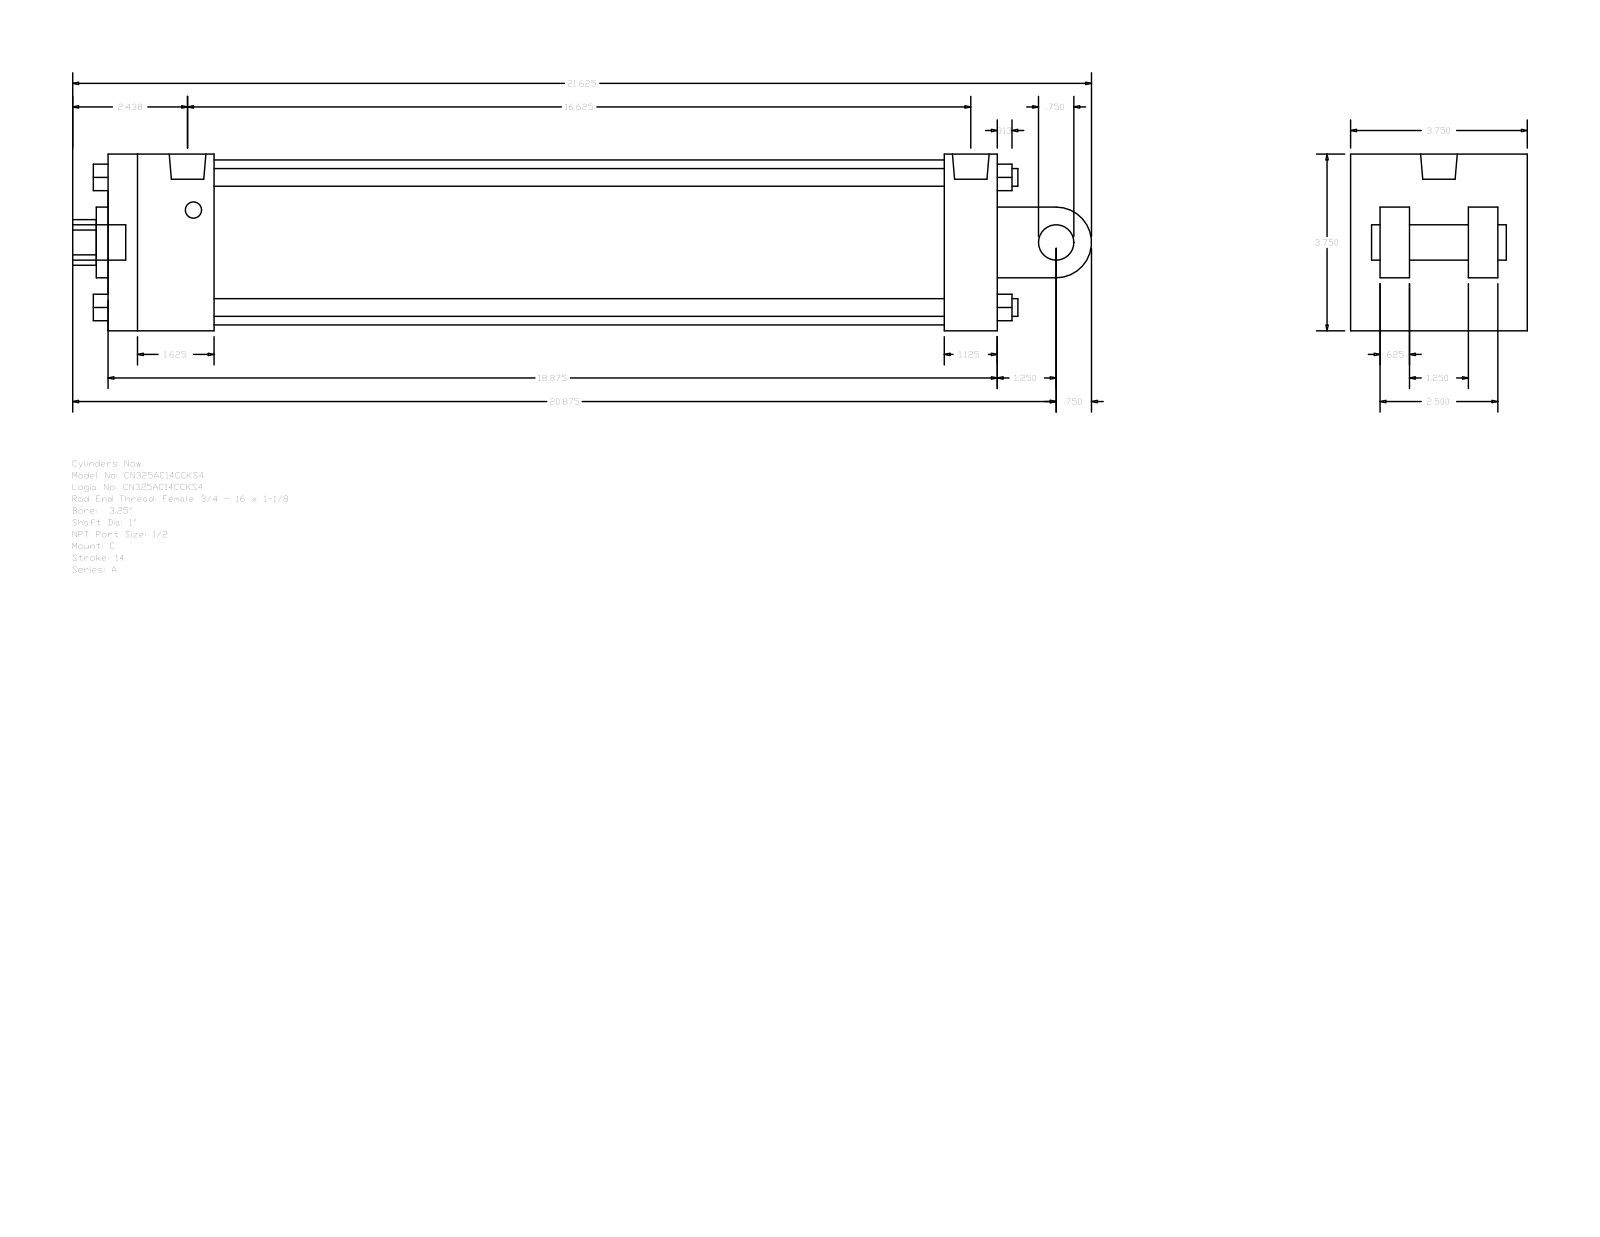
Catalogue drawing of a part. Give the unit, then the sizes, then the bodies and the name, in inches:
Units: inches
Overall size (bounding box): 21.625 × 3.75 × 3.75
Round holes (diameter × count): ⌀0.344 ×2, ⌀0.778 ×1, ⌀1 ×1, ⌀1.5 ×1, ⌀3.5 ×1
Round bosses / shafts (diameter × count): ⌀0.375 ×4, ⌀0.75 ×2, ⌀0.344 ×2, ⌀0.778 ×1
Partial cylindrical surfaces — rounded edges, fillets, slot ends (radius × count): R0.484 ×1, R0.75 ×1
Main face-to-face distances: 3.75, 18.875, 0.625, 2.5, 1.875, 3.125, 1.25, 2.625, 17.75, 1.125
Hole centre spacings: 0.125
Bodies: 0 solids, 135 faces (102 planar, 33 cylindrical, 0 other)
Part name (STEP PRODUCT): A_C__0325_1
STEP written by: GSSL Pune (CONFIG_CONTROL_DESIGN)
